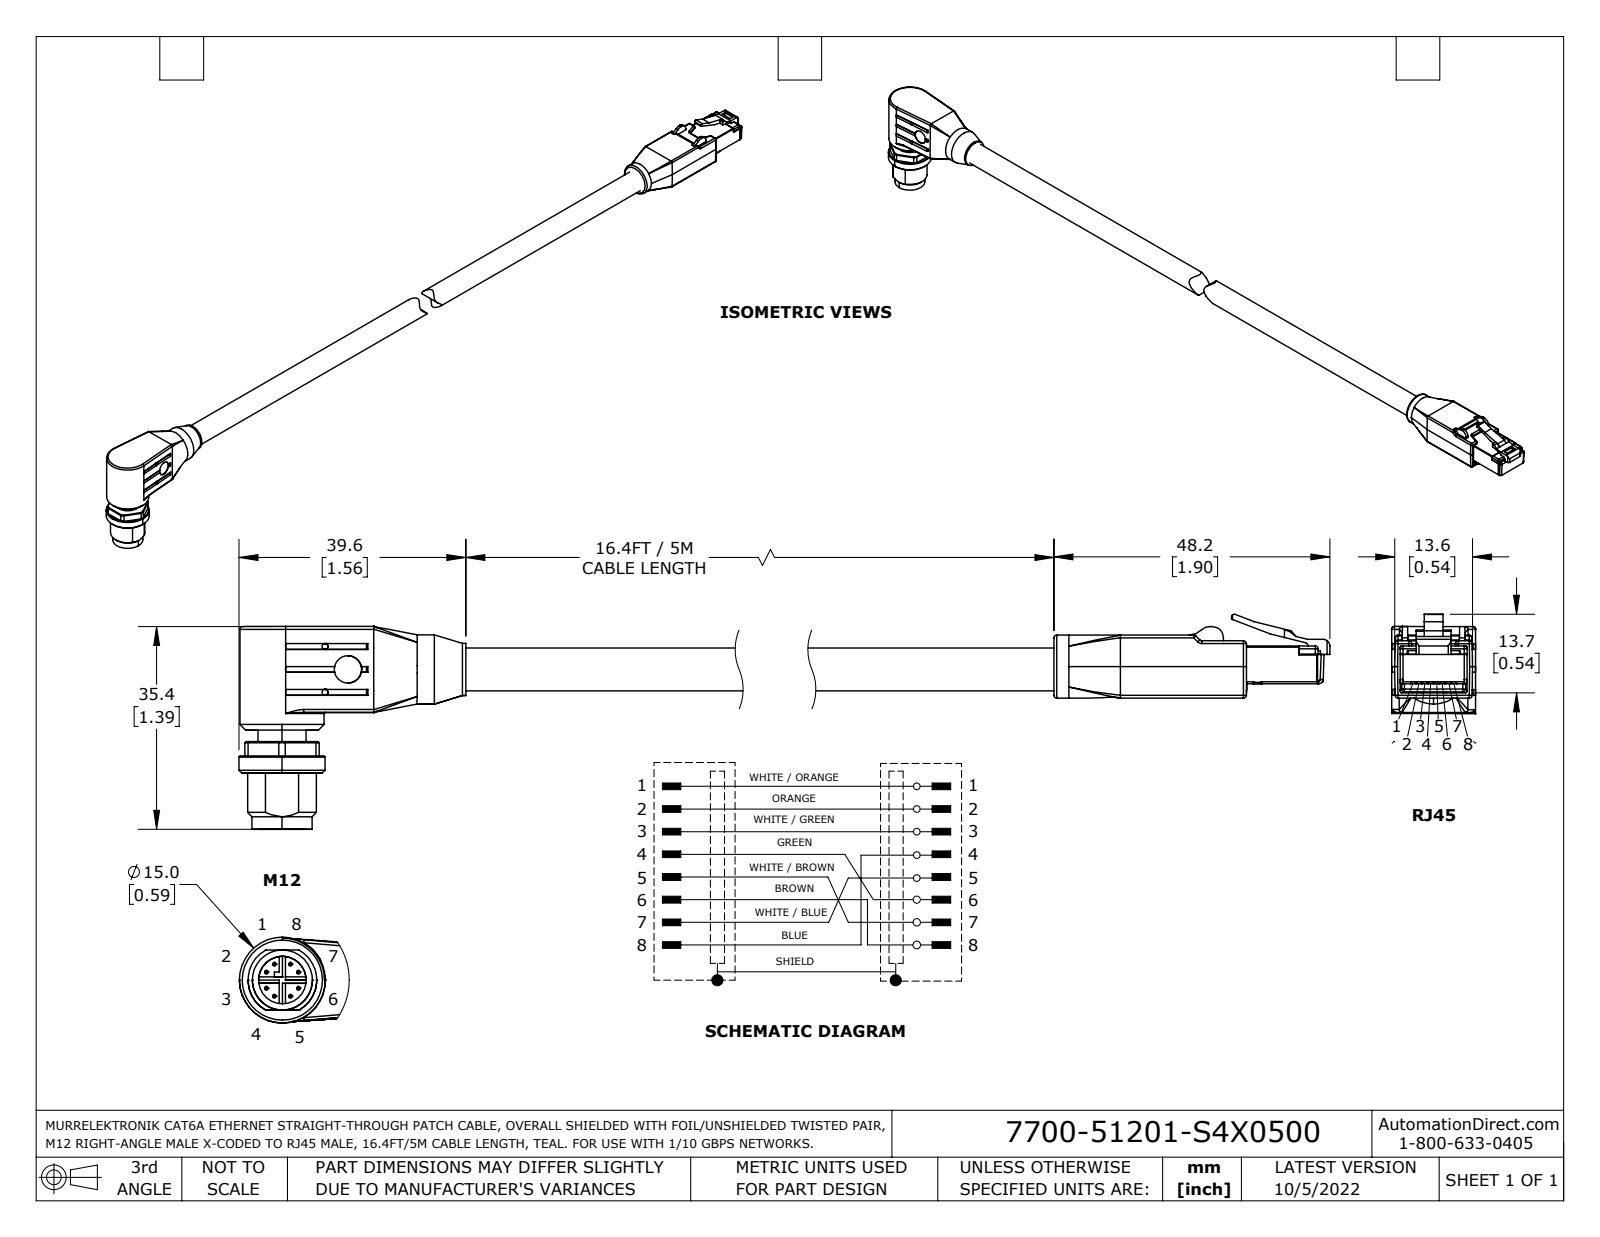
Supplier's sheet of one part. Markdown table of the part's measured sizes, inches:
| quantity | value |
| --- | --- |
| part name | 7700-51201 |
| STEP written by | SolidWorks 2021 (AUTOMOTIVE_DESIGN) |
| units | inches |
| bodies | 5 solids, 586 faces (334 planar, 173 cylindrical, 79 other) |
| overall size | 12.057 × 1.478 × 0.591 |
| volume | 1.552 in³ |
| surface area | 22.58 in² |
| round holes (diameter × count) | 0.041 × 4, 0.189 × 1, 0.327 × 1 |
| round bosses / shafts (diameter × count) | 0.024 × 8, 0.591 × 1, 0.579 × 1, 0.476 × 1, 0.433 × 1, 0.413 × 1, 0.358 × 1, 0.331 × 1 |
| partial cylindrical surfaces (radius × count) | 0.02 × 50, 0.008 × 15, 0.012 × 8, 0.006 × 2, 0.079 × 2, 0.197 × 2, 0.03 × 1, 0.039 × 1 |
| main face-to-face distances | 0.358, 0.035, 0.452, 0.35, 0.535, 0.46, 0.45, 0.442, 0.433, 0.106 |
| hole center spacings | 0.315 |
